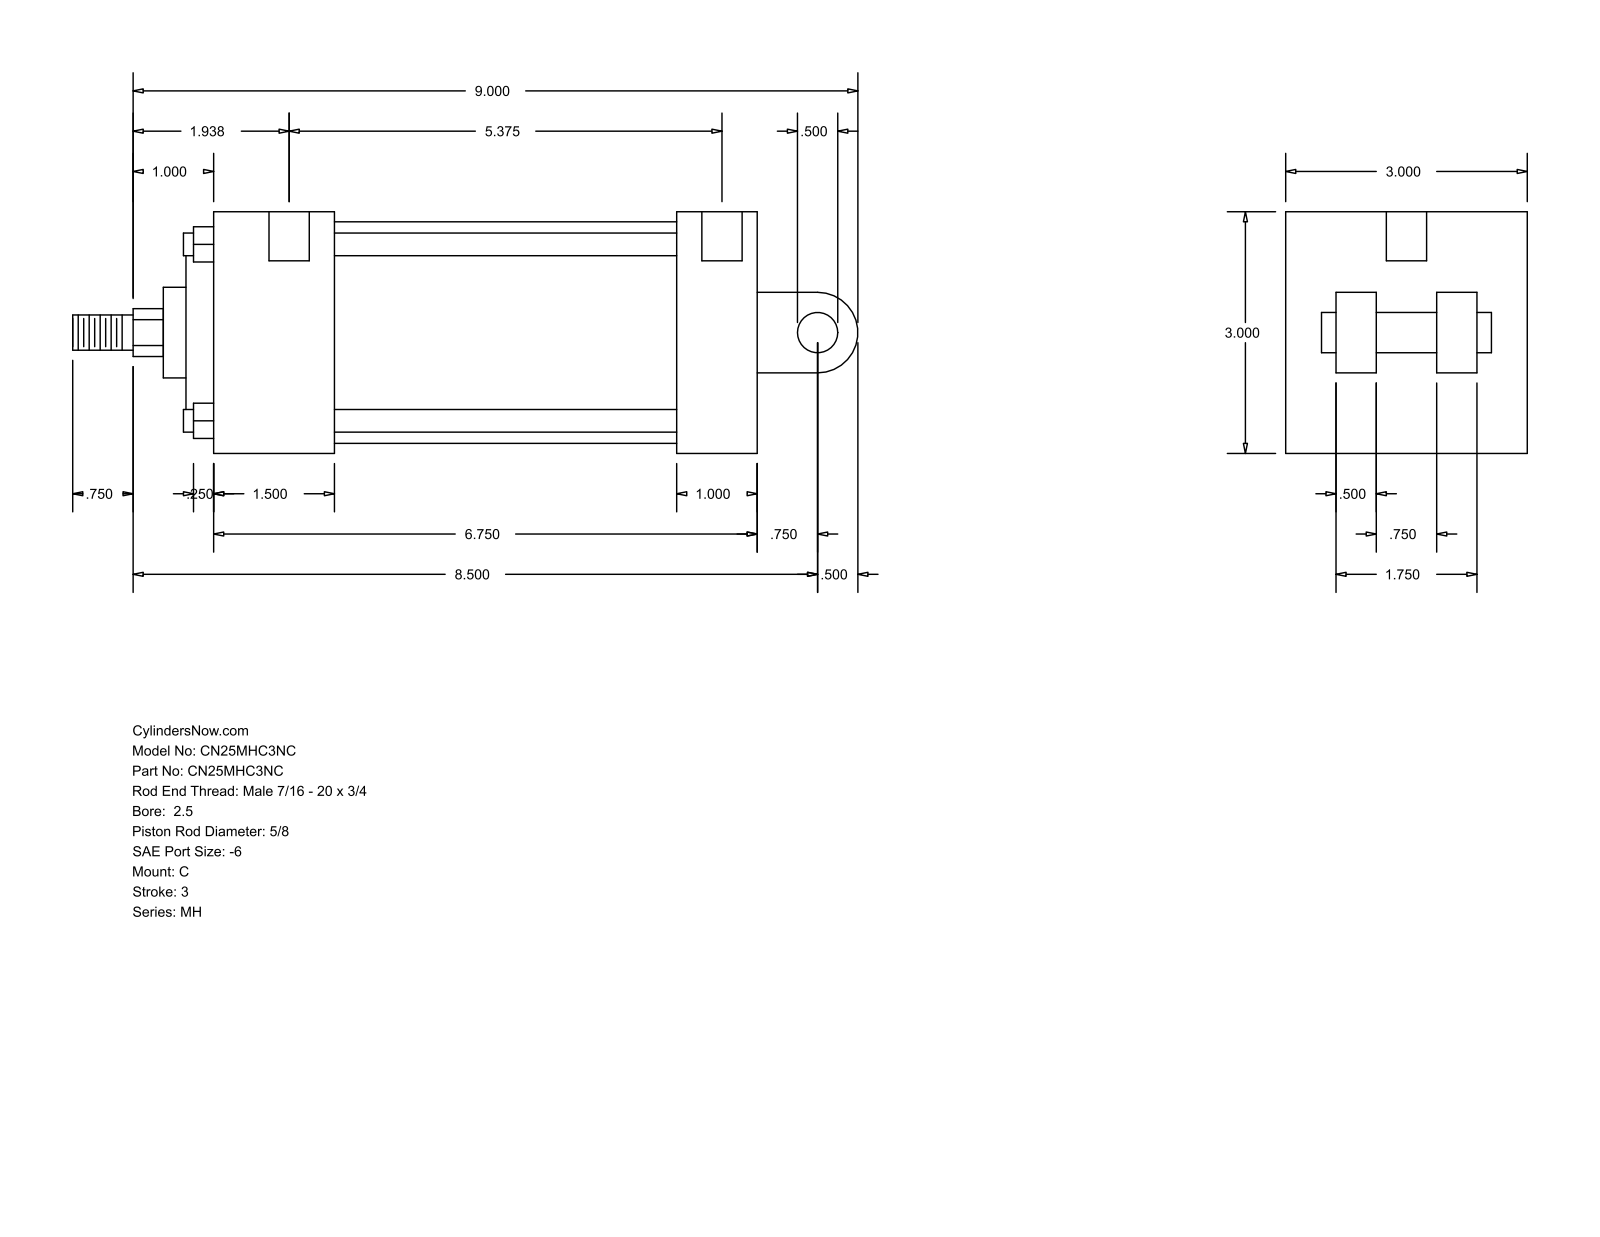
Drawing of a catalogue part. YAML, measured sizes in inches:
part_name: "MH_C__0250_0.625"
step_written_by: "GSSL Pune (CONFIG_CONTROL_DESIGN)"
units: inches
bodies: {solids: 0, faces: 101, planar: 71, cylindrical: 30, other: 0}
overall_size: [9.75, 3, 3]
round_holes:
  - {diameter: 0.219, count: 4}
  - {diameter: 0.5, count: 2}
round_bosses_or_shafts:
  - {diameter: 0.281, count: 4}
  - {diameter: 2.75, count: 1}
  - {diameter: 2.187, count: 1}
  - {diameter: 1.125, count: 1}
  - {diameter: 0.625, count: 1}
  - {diameter: 0.5, count: 1}
  - {diameter: 0.437, count: 1}
partial_cylinders:
  - {radius: 0.297, count: 1}
  - {radius: 0.5, count: 1}
face_to_face_distances: [3, 1, 6.75, 0.625, 1.5, 5.75, 4.25, 5.25, 0.344, 1.844]
hole_center_spacings: [5.687, 0.125, 0.187, 5.375, 5.5, 5.563]
